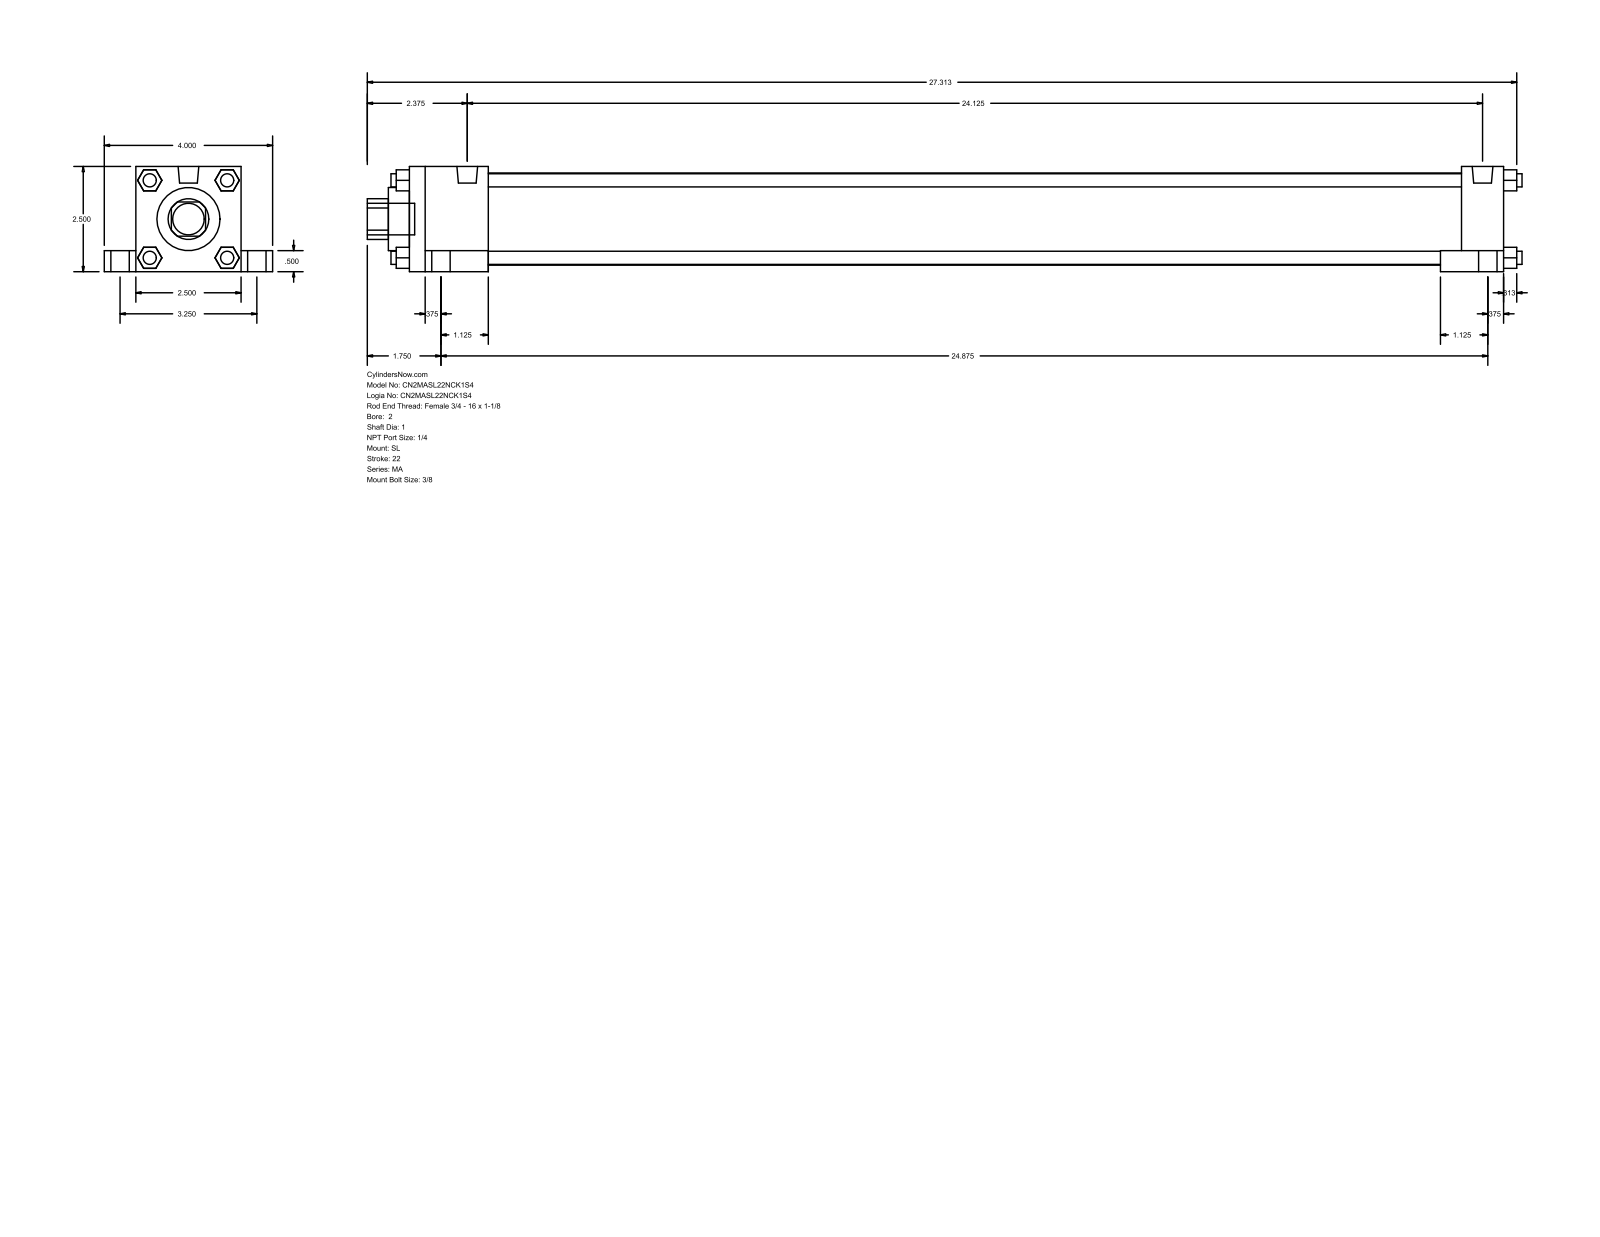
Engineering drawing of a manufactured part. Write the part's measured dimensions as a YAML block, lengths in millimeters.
part_name: "MA_SL__0200_1"
step_written_by: "GSSL Pune (CONFIG_CONTROL_DESIGN)"
units: millimeters
bodies: {solids: 0, faces: 148, planar: 112, cylindrical: 36, other: 0}
overall_size: [696.91, 101.6, 63.5]
round_holes:
  - {diameter: 25.4, count: 1}
  - {diameter: 38.1, count: 1}
  - {diameter: 55.63, count: 1}
round_bosses_or_shafts:
  - {diameter: 7.94, count: 8}
  - {diameter: 17.46, count: 4}
  - {diameter: 11.11, count: 4}
  - {diameter: 12.49, count: 2}
  - {diameter: 19.05, count: 1}
partial_cylinders:
  - {radius: 12.29, count: 1}
face_to_face_distances: [63.5, 12.7, 660.4, 19.05, 82.55, 25.4, 50.8, 47.63, 612.77, 635]
